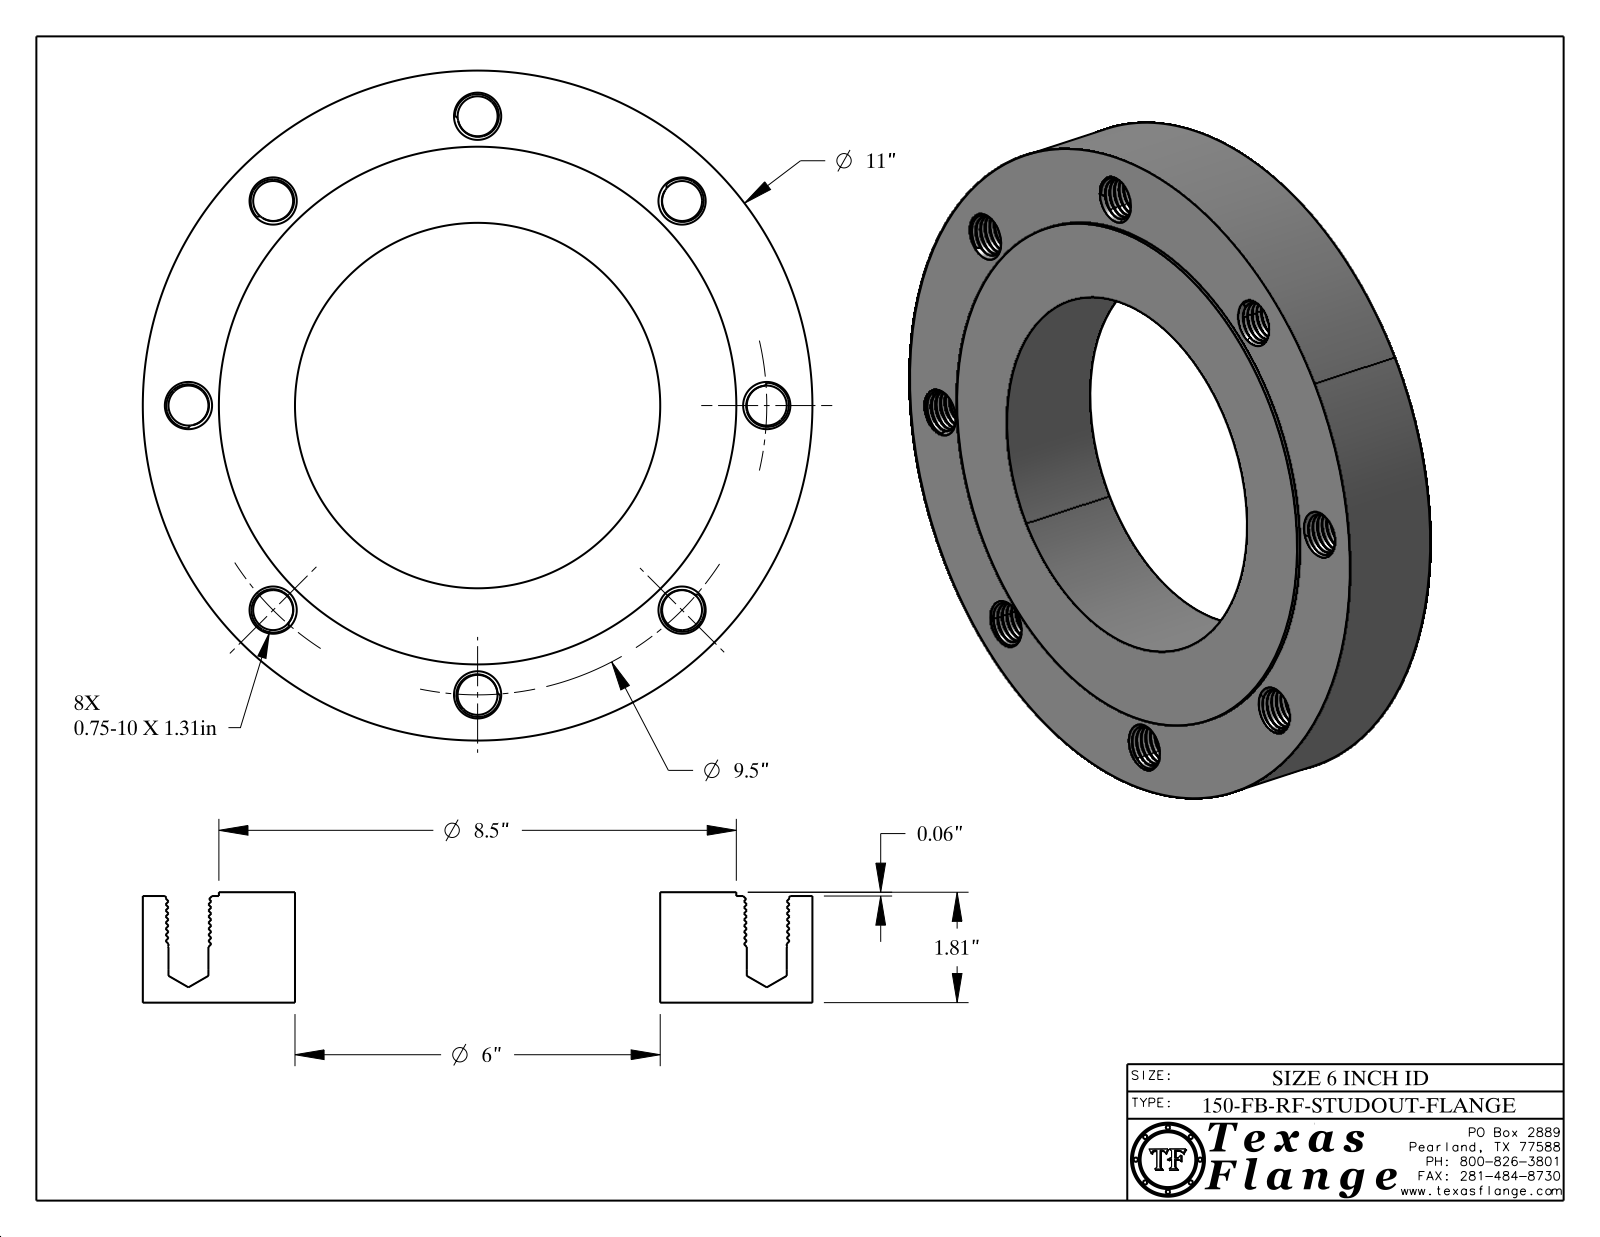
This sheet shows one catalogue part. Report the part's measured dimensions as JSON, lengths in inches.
{"part_name": "6-150-FB-RF-STUDOUT-FLANGE", "step_written_by": "CATIA V5 STEP AP214 (AUTOMOTIVE_DESIGN)", "units": "inches", "bodies": {"solids": 1, "faces": 874, "planar": 368, "cylindrical": 186, "other": 320}, "overall_size": [11, 11, 1.813], "volume_in3": 114.5, "surface_area_in2": 257.6, "round_holes": [[0.656, 8], [1, 1], [6, 1]], "round_bosses_or_shafts": [[0.061, 8], [11, 1], [8.5, 1], [0.788, 1]], "face_to_face_distances": [1.75, 0.063, 1.813, 1.798, 1.735, 0.015, 0.298, 0.293, 0.054, 0.248], "hole_center_spacings": [3.635, 4.75, 6.717, 8.777, 9.5, 9.5]}
